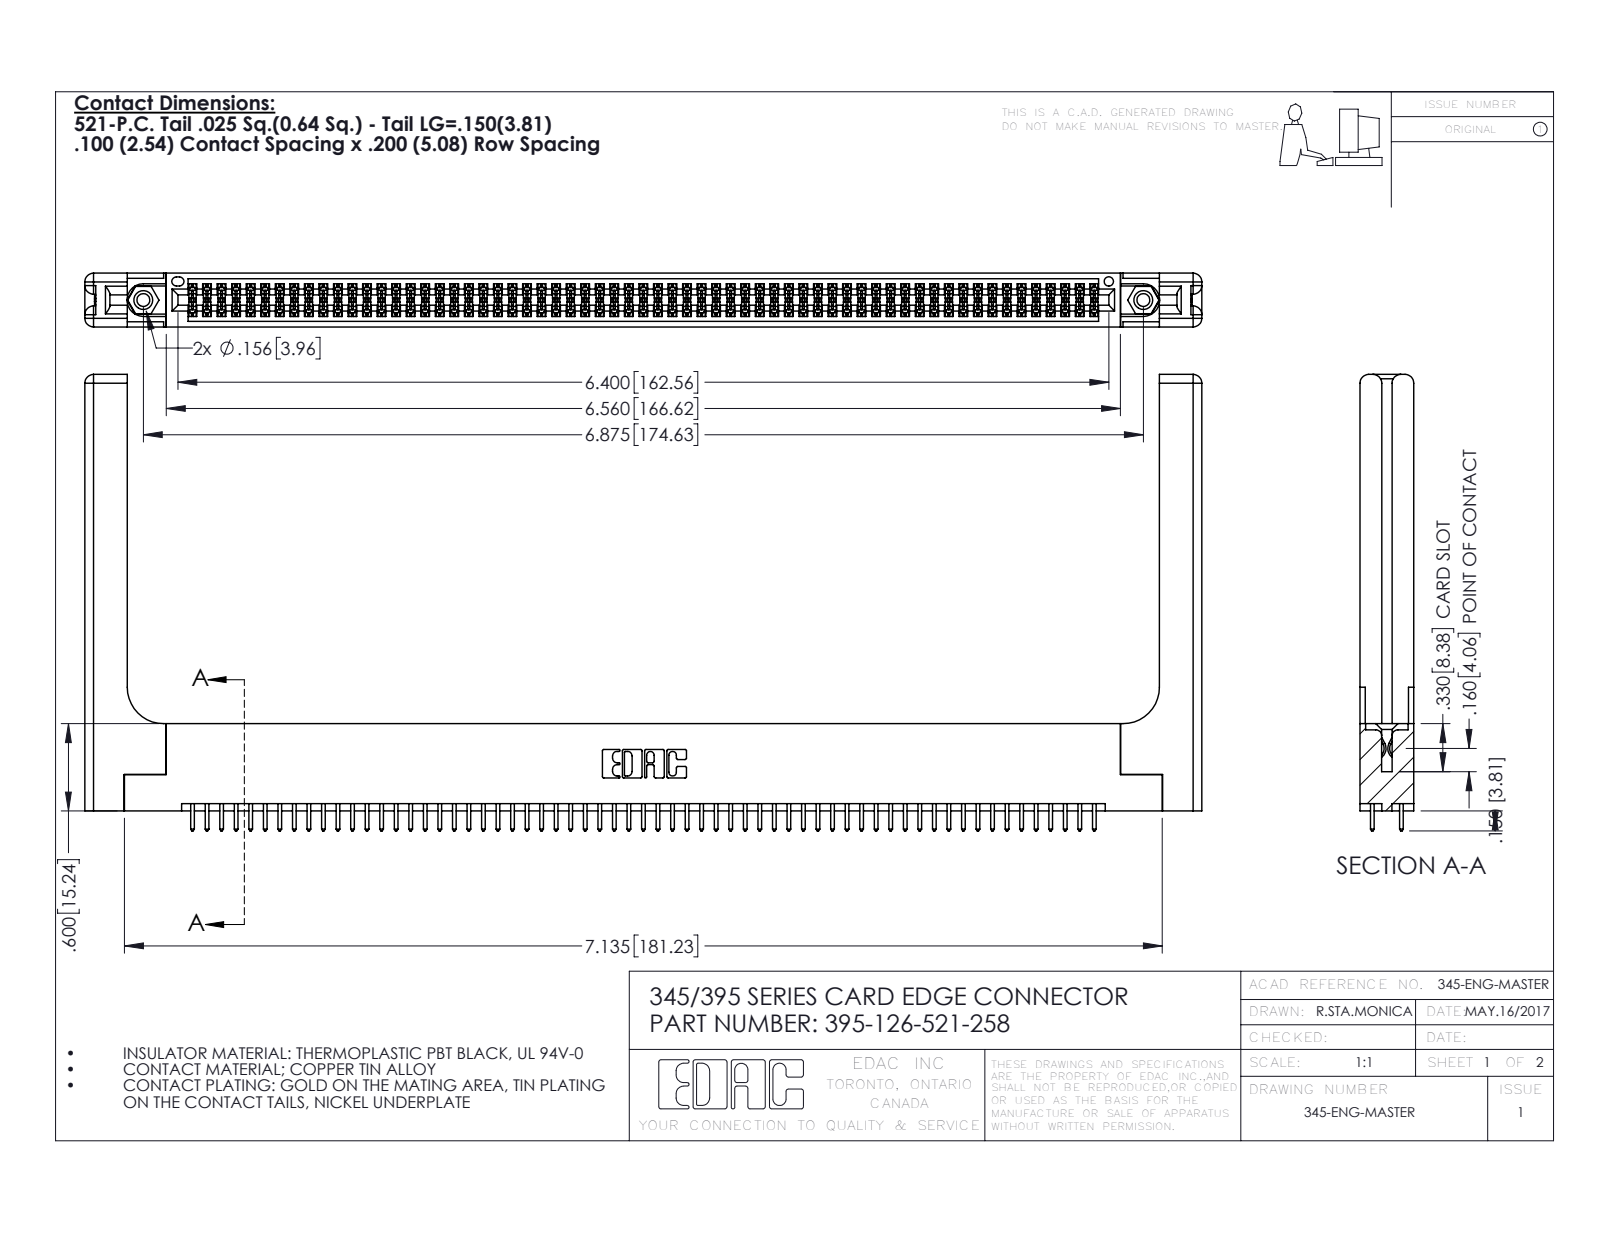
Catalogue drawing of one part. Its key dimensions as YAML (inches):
part_name: "345-292-001_345-293-121; 345 Part_Flush Mounting Lugs - 0.156 Dia-TH; 395-126-521-258; 345-250-001_345-250-001-102 (+1 more)"
step_written_by: "SolidWorks 2016 (CONFIG_CONTROL_DESIGN)"
units: inches
bodies: {solids: 131, faces: 6682, planar: 4386, cylindrical: 2236, other: 60}
overall_size: [7.679, 3.137, 0.37]
volume: 1.682
surface_area: 51.69
round_holes:
  - {diameter: 0.089, count: 2}
  - {diameter: 0.125, count: 2}
  - {diameter: 0.156, count: 2}
  - {diameter: 0.064, count: 1}
round_bosses_or_shafts:
  - {diameter: 0.155, count: 2}
partial_cylinders:
  - {radius: 0.006, count: 189}
  - {radius: 0.01, count: 126}
  - {radius: 0.01, count: 22}
  - {radius: 0.06, count: 16}
  - {radius: 0.007, count: 6}
  - {radius: 0.031, count: 6}
  - {radius: 0.026, count: 3}
  - {radius: 0.014, count: 2}
face_to_face_distances: [0.072, 0.298, 0.37, 0.2, 0.098, 0.272, 0.025, 0.225, 0.175, 0.148]
hole_center_spacings: [0.27, 6.639, 6.875]
